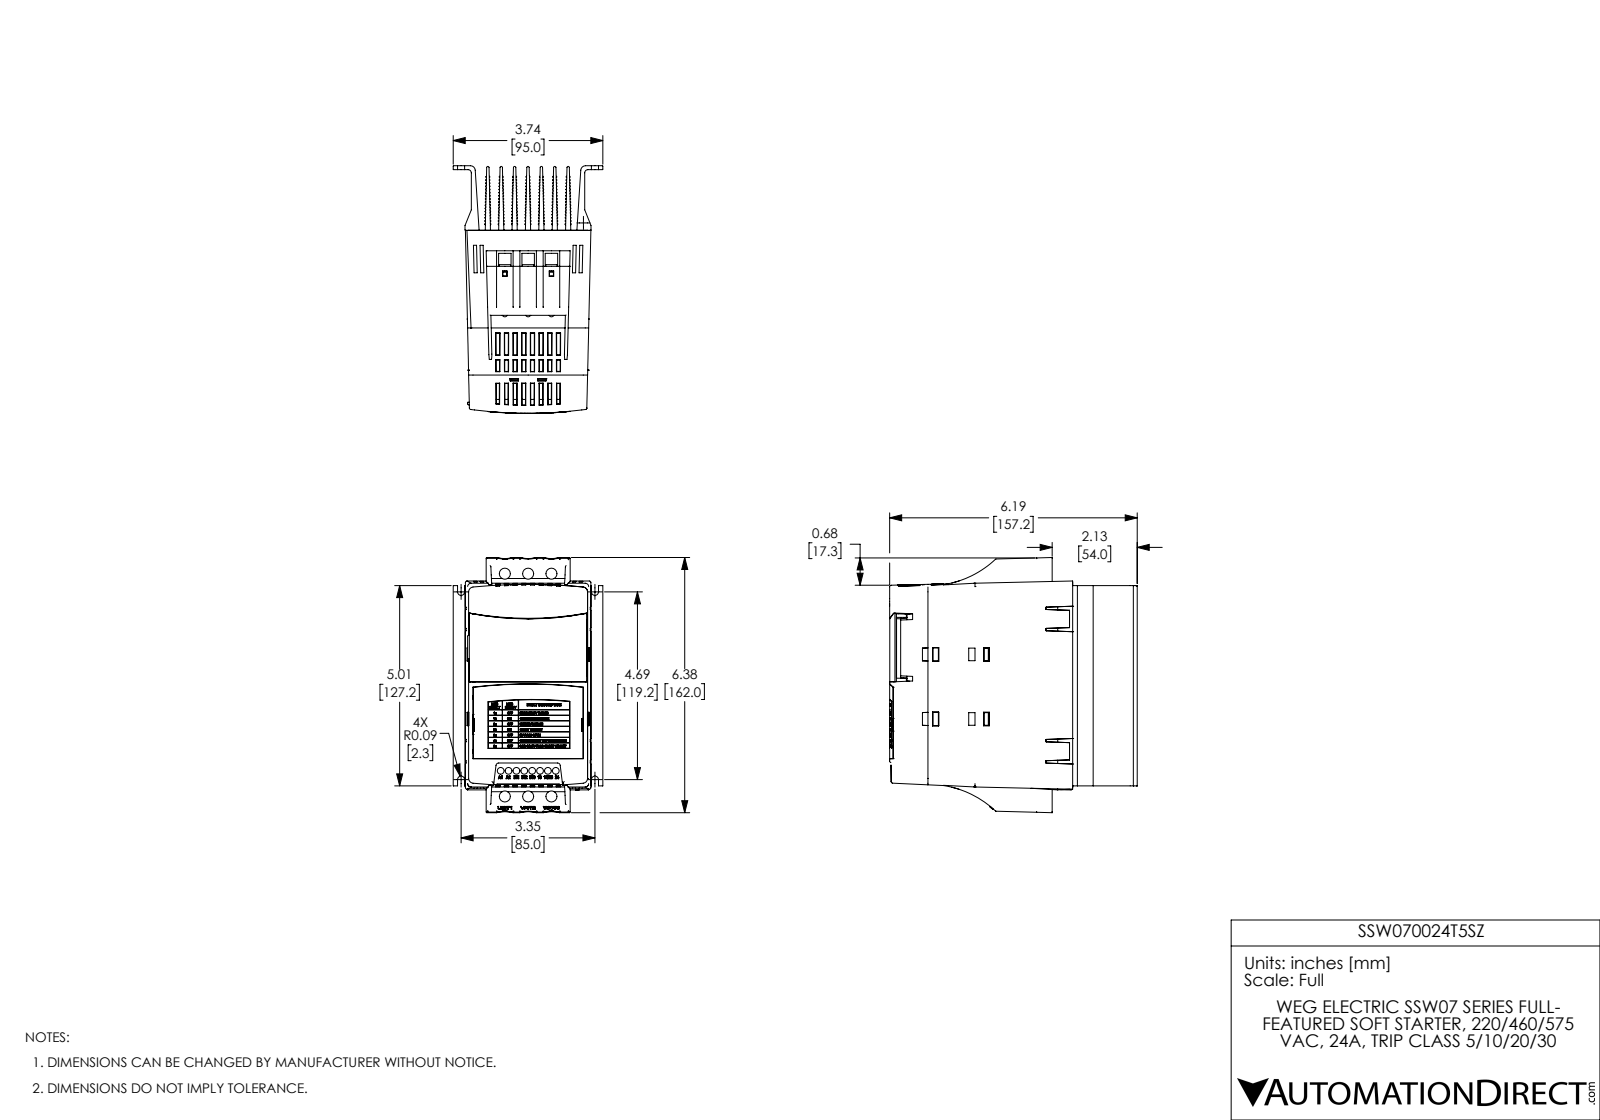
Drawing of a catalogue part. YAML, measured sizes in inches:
part_name: "SSW07 MEC A mod 1 ext1 B3b Coord 1"
step_written_by: "SolidWorks 2017 (AUTOMOTIVE_DESIGN)"
units: inches
bodies: {solids: 1, faces: 5830, planar: 3882, cylindrical: 813, other: 1135}
overall_size: [6.38, 6.193, 3.74]
volume: 76.19
surface_area: 424.3
round_holes:
  - {diameter: 0.276, count: 6}
  - {diameter: 0.071, count: 4}
  - {diameter: 0.13, count: 1}
  - {diameter: 0.256, count: 1}
round_bosses_or_shafts:
  - {diameter: 0.283, count: 1}
partial_cylinders:
  - {radius: 0.016, count: 224}
  - {radius: 0.02, count: 18}
  - {radius: 0.008, count: 17}
  - {radius: 0.787, count: 12}
  - {radius: 0.03, count: 7}
  - {radius: 0.039, count: 7}
  - {radius: 0.012, count: 6}
  - {radius: 0.024, count: 5}
face_to_face_distances: [0.335, 0.669, 1.004, 1.339, 0.335, 0.334, 1.673, 0.67, 0.669, 1.004]
hole_center_spacings: [0.583, 0.325, 0.326, 5.431, 5.433, 5.601, 5.57, 0.886]
